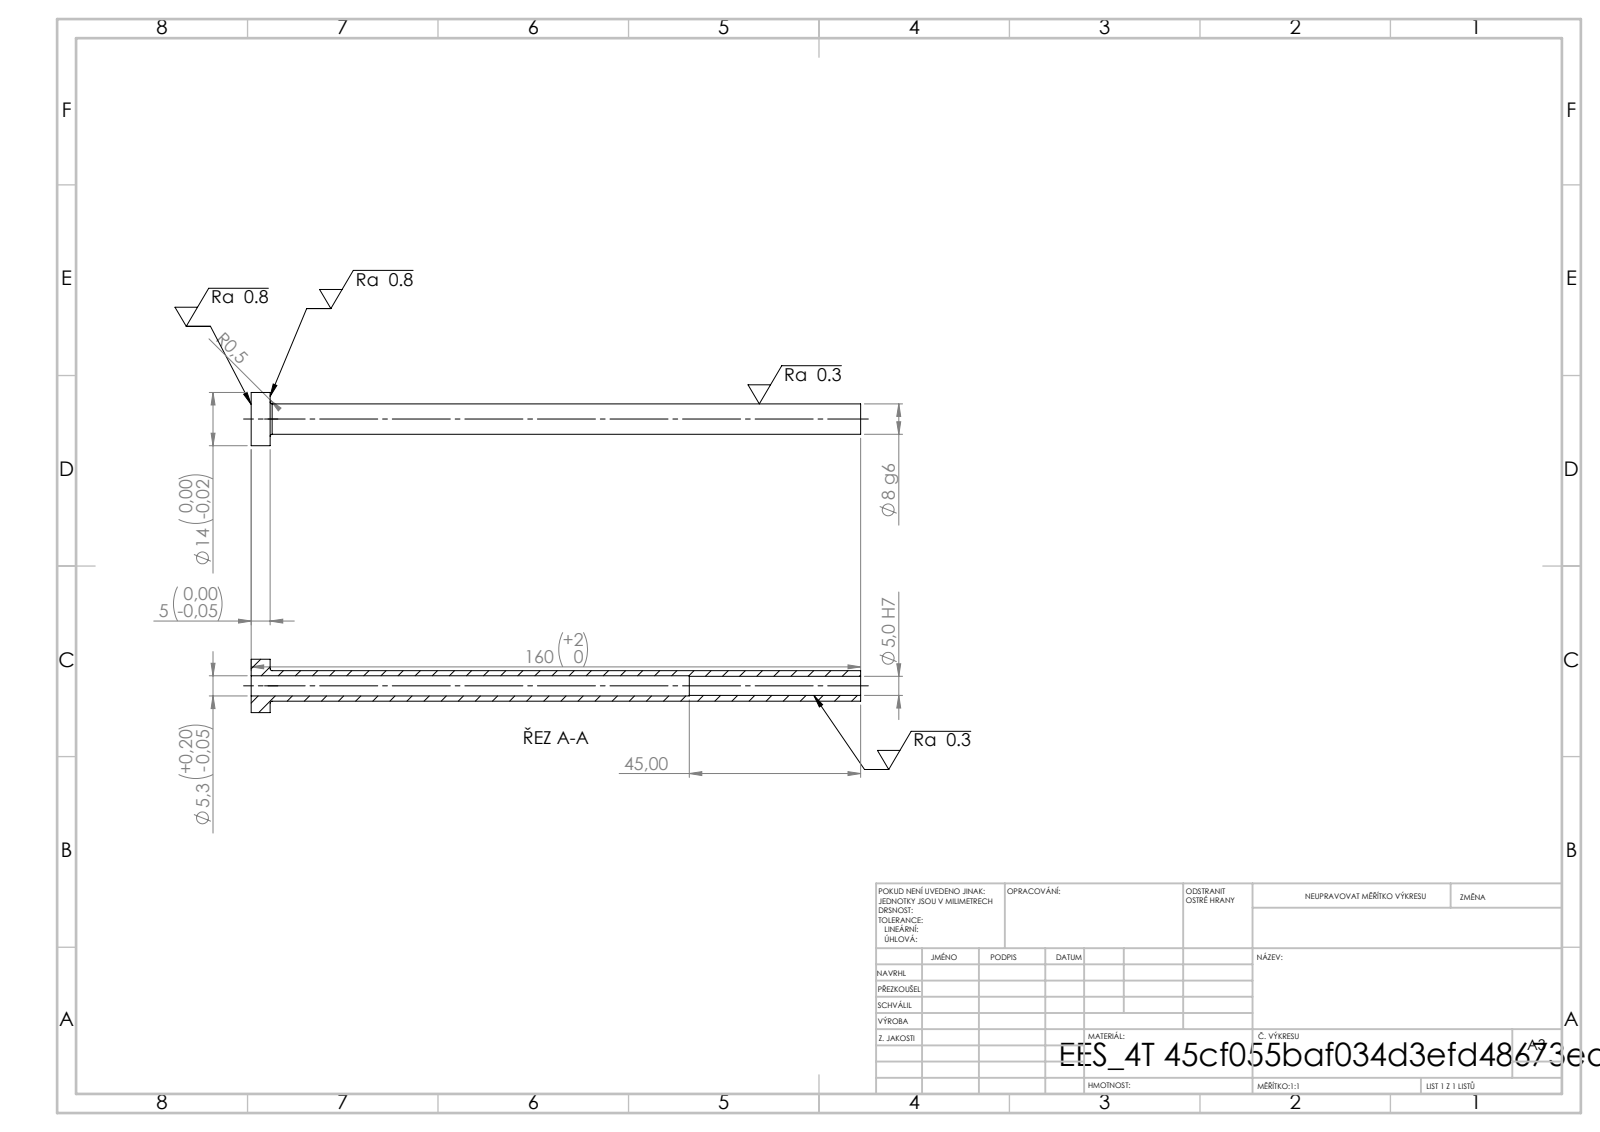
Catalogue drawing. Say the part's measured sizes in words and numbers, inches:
Its 3-D file was written by "SolidWorks 2019 (CONFIG_CONTROL_DESIGN)". It is 1 solid with 14 faces: 4 planar, 8 cylindrical and 2 other. Overall it measures 6.299 by 0.551 by 0.551 inches. Its volume is 0.314 cubic inches and its surface area 10.85 square inches. Round holes: 1 of diameter 0.197, 1 of diameter 0.209. Round bosses or shafts: 1 of diameter 0.551, 1 of diameter 0.315. The main face-to-face distances are 0.197, 6.299, 6.102, 4.528, 4.331, 1.772.
